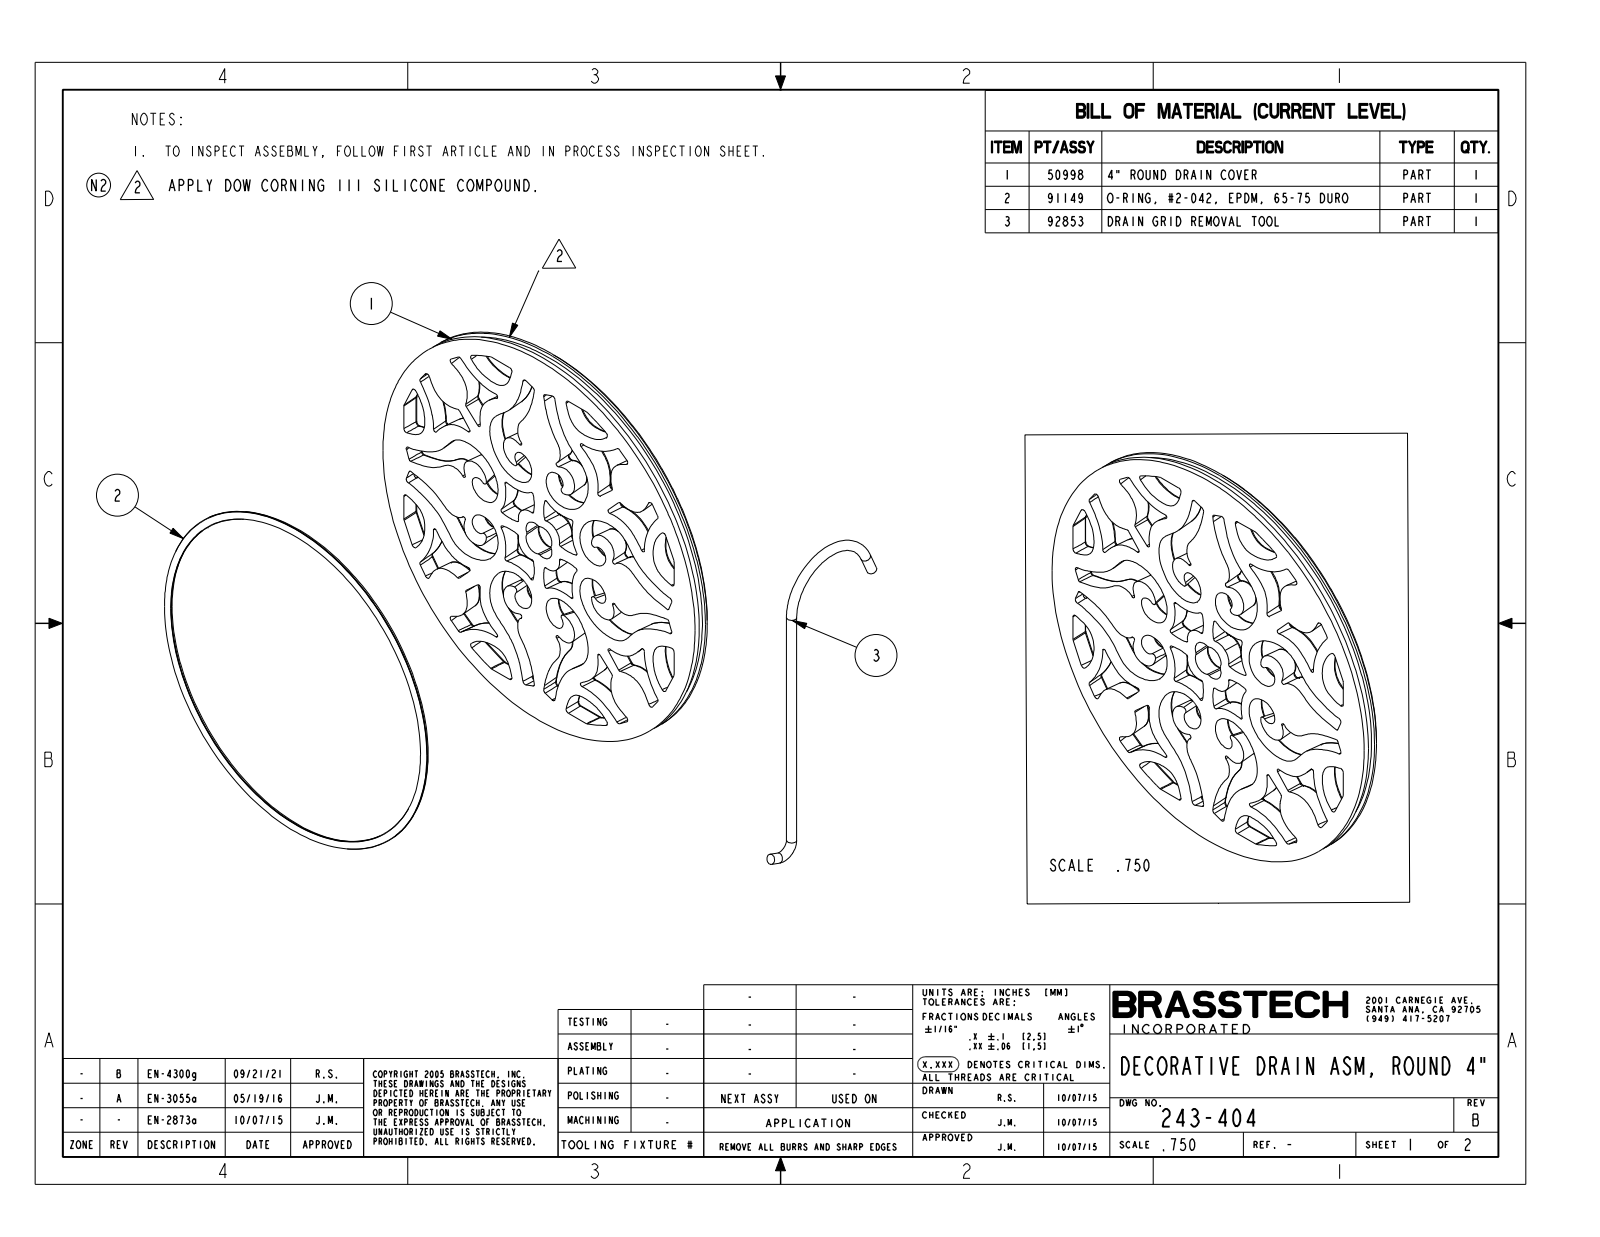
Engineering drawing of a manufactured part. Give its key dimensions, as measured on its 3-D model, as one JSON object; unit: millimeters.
{"part_name": "50998; 243-404_ASM", "step_written_by": "CREO PARAMETRIC BY PTC INC, 2018400 (CONFIG_CONTROL_DESIGN)", "units": "millimeters", "bodies": {"solids": 1, "faces": 1625, "planar": 108, "cylindrical": 138, "other": 1379}, "overall_size": [102.6, 102.6, 4.8], "volume_mm3": 22300, "surface_area_mm2": 57940, "round_bosses_or_shafts": [[102.6, 1], [100.7, 1], [100.6, 1]], "partial_cylinders_radius": [[0.5, 26], [0.5, 19], [0.8, 4], [47.6, 1]], "face_to_face_distances": [4.8, 1.4, 3.4, 1.4, 3.4, 2, 2, 2]}
